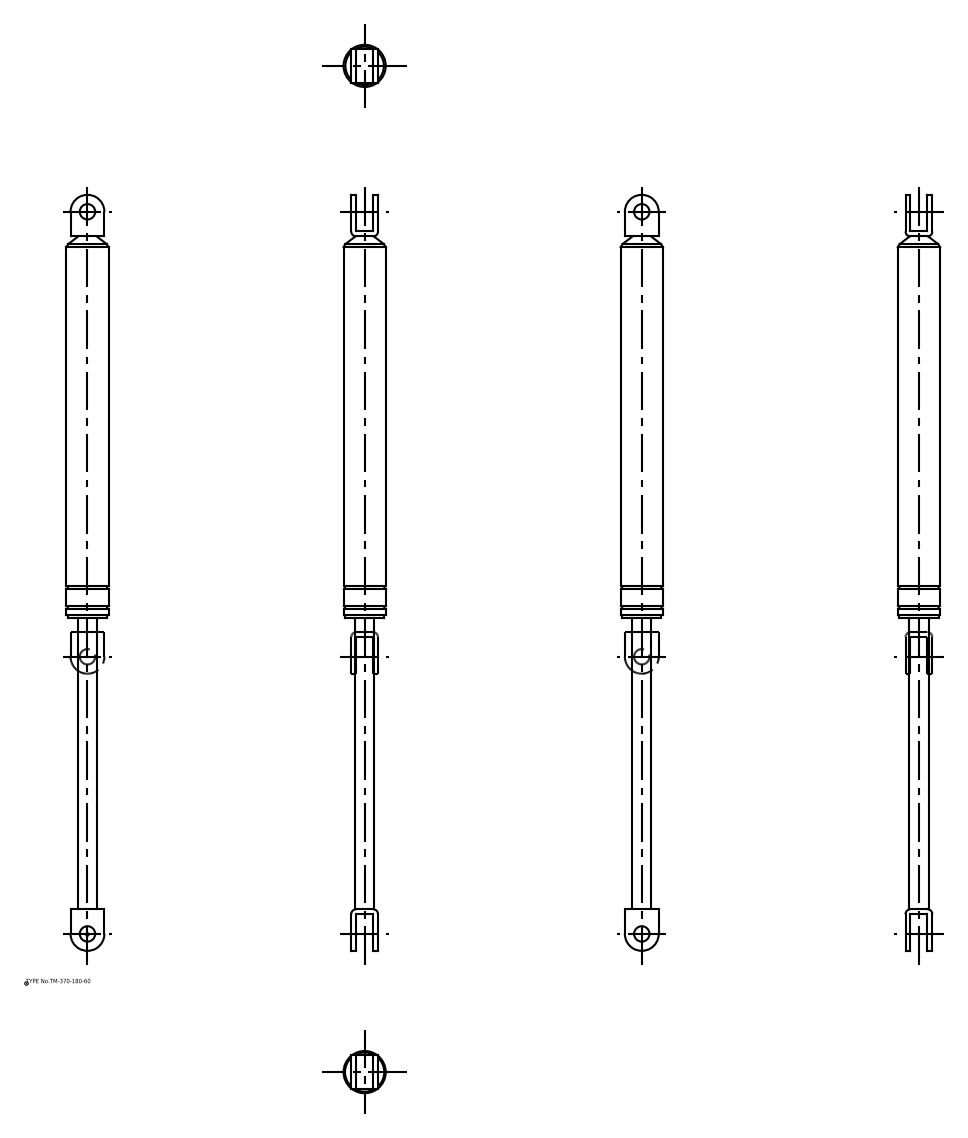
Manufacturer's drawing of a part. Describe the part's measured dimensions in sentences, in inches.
The part is named "TM_370_180_60; TM_370_180_60_div". Its 3-D file was written by "spGate 16.7.1 (AUTOMOTIVE_DESIGN)". It is 2 solids with 64 faces: 22 planar, 32 cylindrical and 10 other. Overall it measures 19.331 by 1.11 by 1.11 inches. Its volume is 10.69 cubic inches and its surface area 55.1 square inches. Round holes: 2 of diameter 0.394. Round bosses or shafts: 1 of diameter 1.11, 1 of diameter 1.079, 1 of diameter 1.004, 1 of diameter 0.492. Partial cylindrical surfaces (rounded edges, fillets, slot ends): 4 of radius 0.126, 2 of radius 0.433. The main face-to-face distances are 0.126, 0.559, 0.685, 0.433, 0.866, 17.331, 7.567, 17.457, 9.89, 9.764. The hole center spacings are 18.465.
